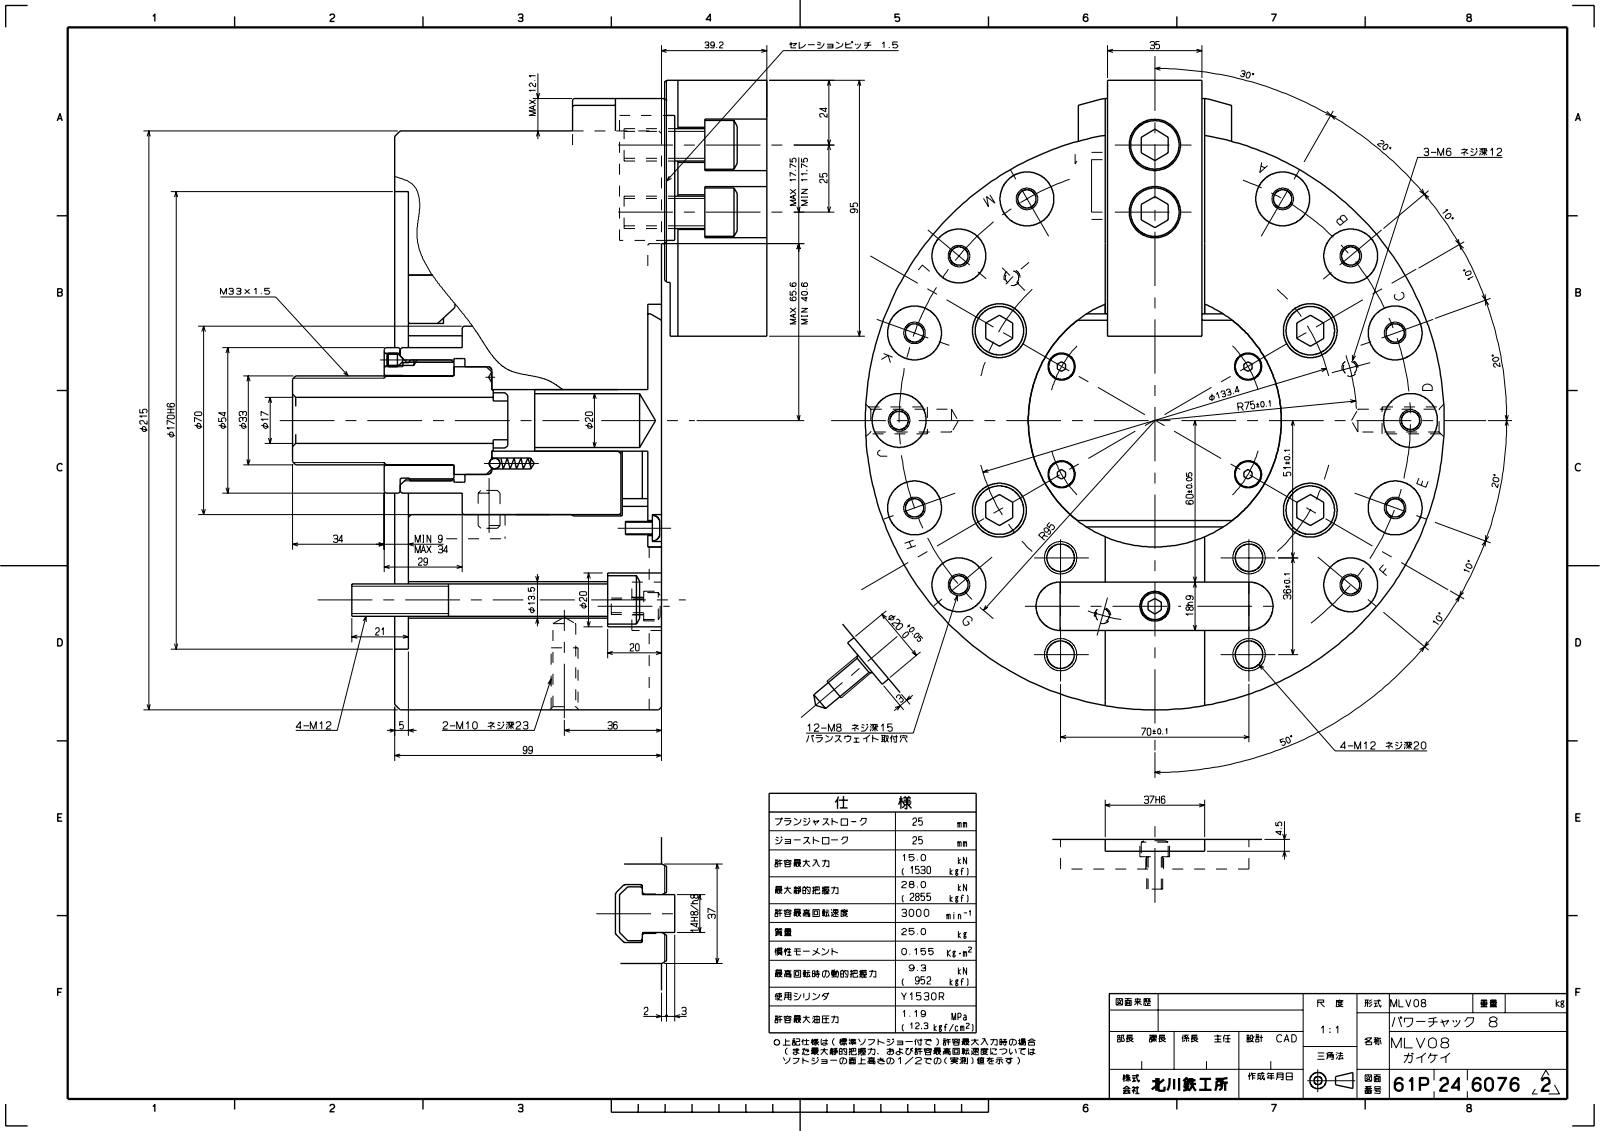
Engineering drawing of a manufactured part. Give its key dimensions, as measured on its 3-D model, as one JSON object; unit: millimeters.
{"part_name": "61P245482_MLV08_ASSY", "step_written_by": "ST-DEVELOPER v16.7 (AUTOMOTIVE_DESIGN)", "units": "millimeters", "bodies": {"solids": 15, "faces": 964, "planar": 857, "cylindrical": 64, "other": 43}, "overall_size": [206.59, 133.2, 110], "volume_mm3": 258876, "surface_area_mm2": 86952, "round_holes": [[5.5, 4], [10, 4], [13, 2], [19, 2], [4.4, 1], [5, 1], [6, 1], [15, 1], [16, 1], [20, 1]], "round_bosses_or_shafts": [[9.5, 4], [5, 4], [18, 3], [13, 2], [12, 2], [8, 2], [6, 2], [23, 1]], "partial_cylinders_radius": [[0.4, 2], [3, 2], [6, 2], [8, 2], [7.3, 1], [10.75, 1], [30, 1], [47, 1]], "face_to_face_distances": [5, 10, 39.2, 35, 33, 12, 16, 17, 21.5, 1], "hole_center_spacings": [40, 69.28, 72.41, 80, 95.12, 109.23, 133.17, 25]}
